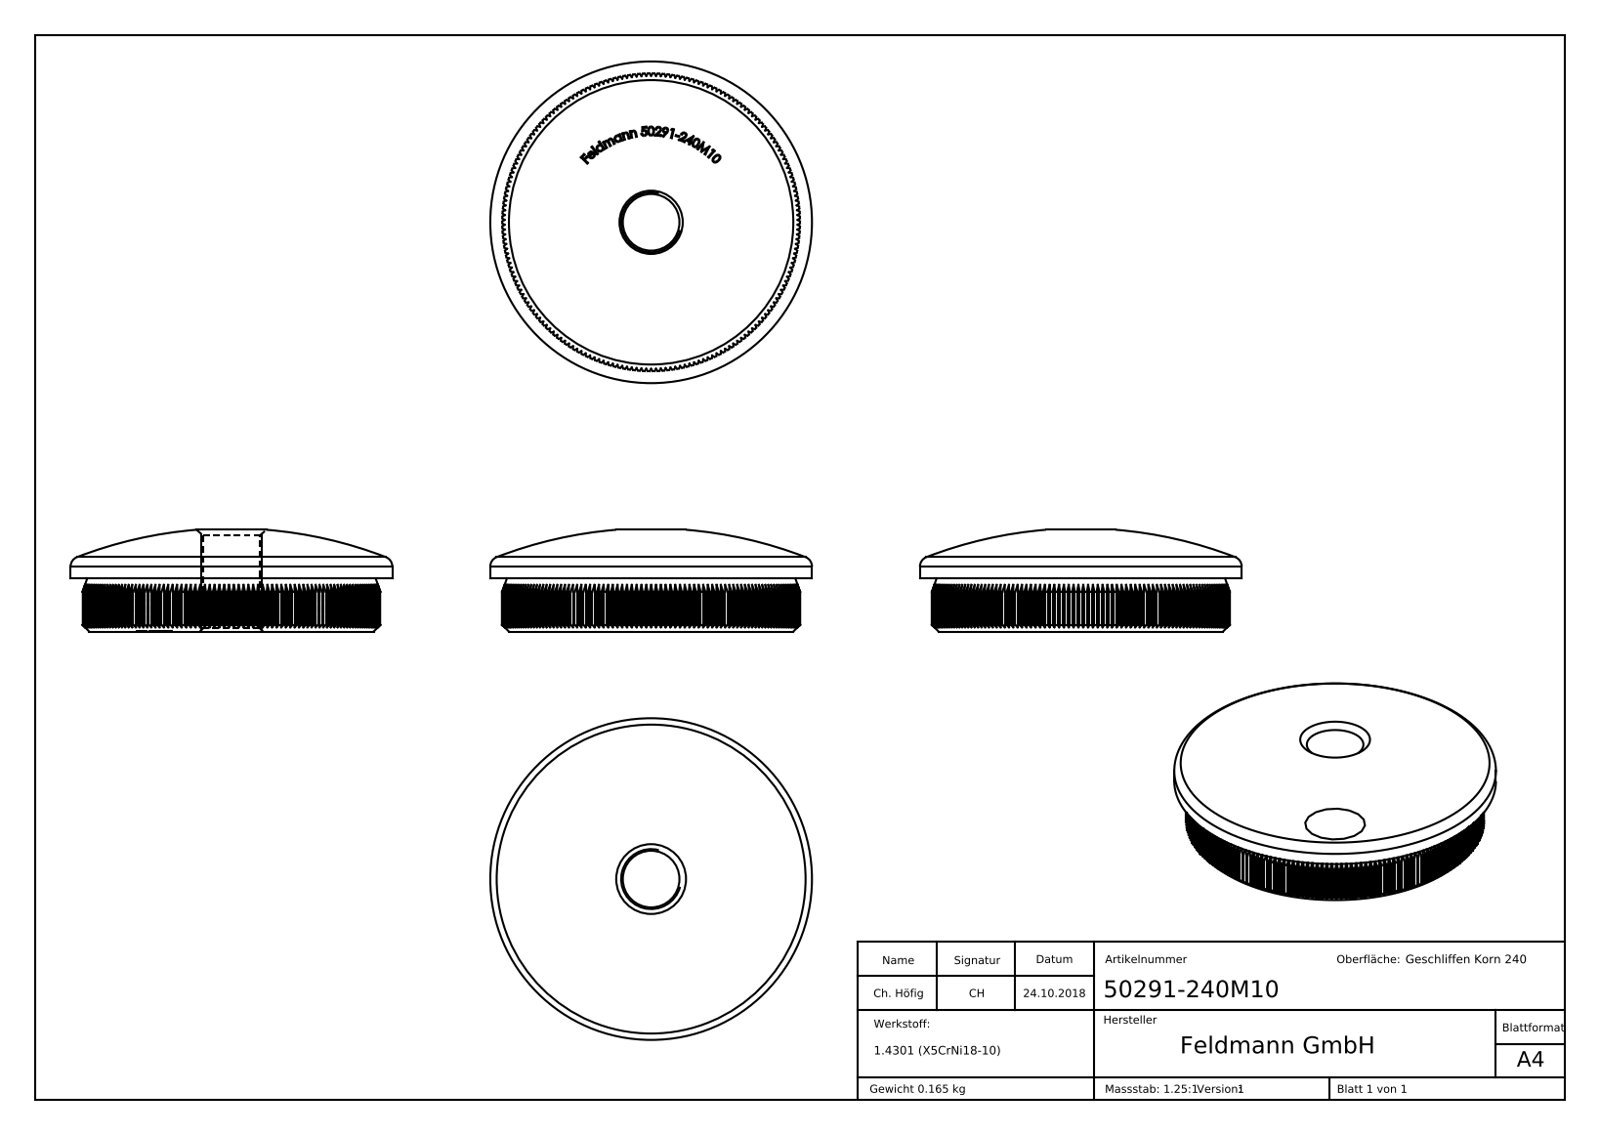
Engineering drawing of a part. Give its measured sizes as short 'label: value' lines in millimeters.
name: 50291-240M10
written by: SolidWorks 2015 (CONFIG_CONTROL_DESIGN)
unit: mm
bodies: 1 solid, 813 faces (512 planar, 194 cylindrical, 107 other)
size: 48.3 × 48.3 × 15.29
volume: 20 884 mm³; area: 5 979 mm²
holes: 1× ⌀8.5
bosses: 1× ⌀48.3
rounds: 1× R22.35
face distances: 8, 22, 21.98, 22.02, 7.9, 0.66, 0.54, 0.67, 0.79, 0.72
